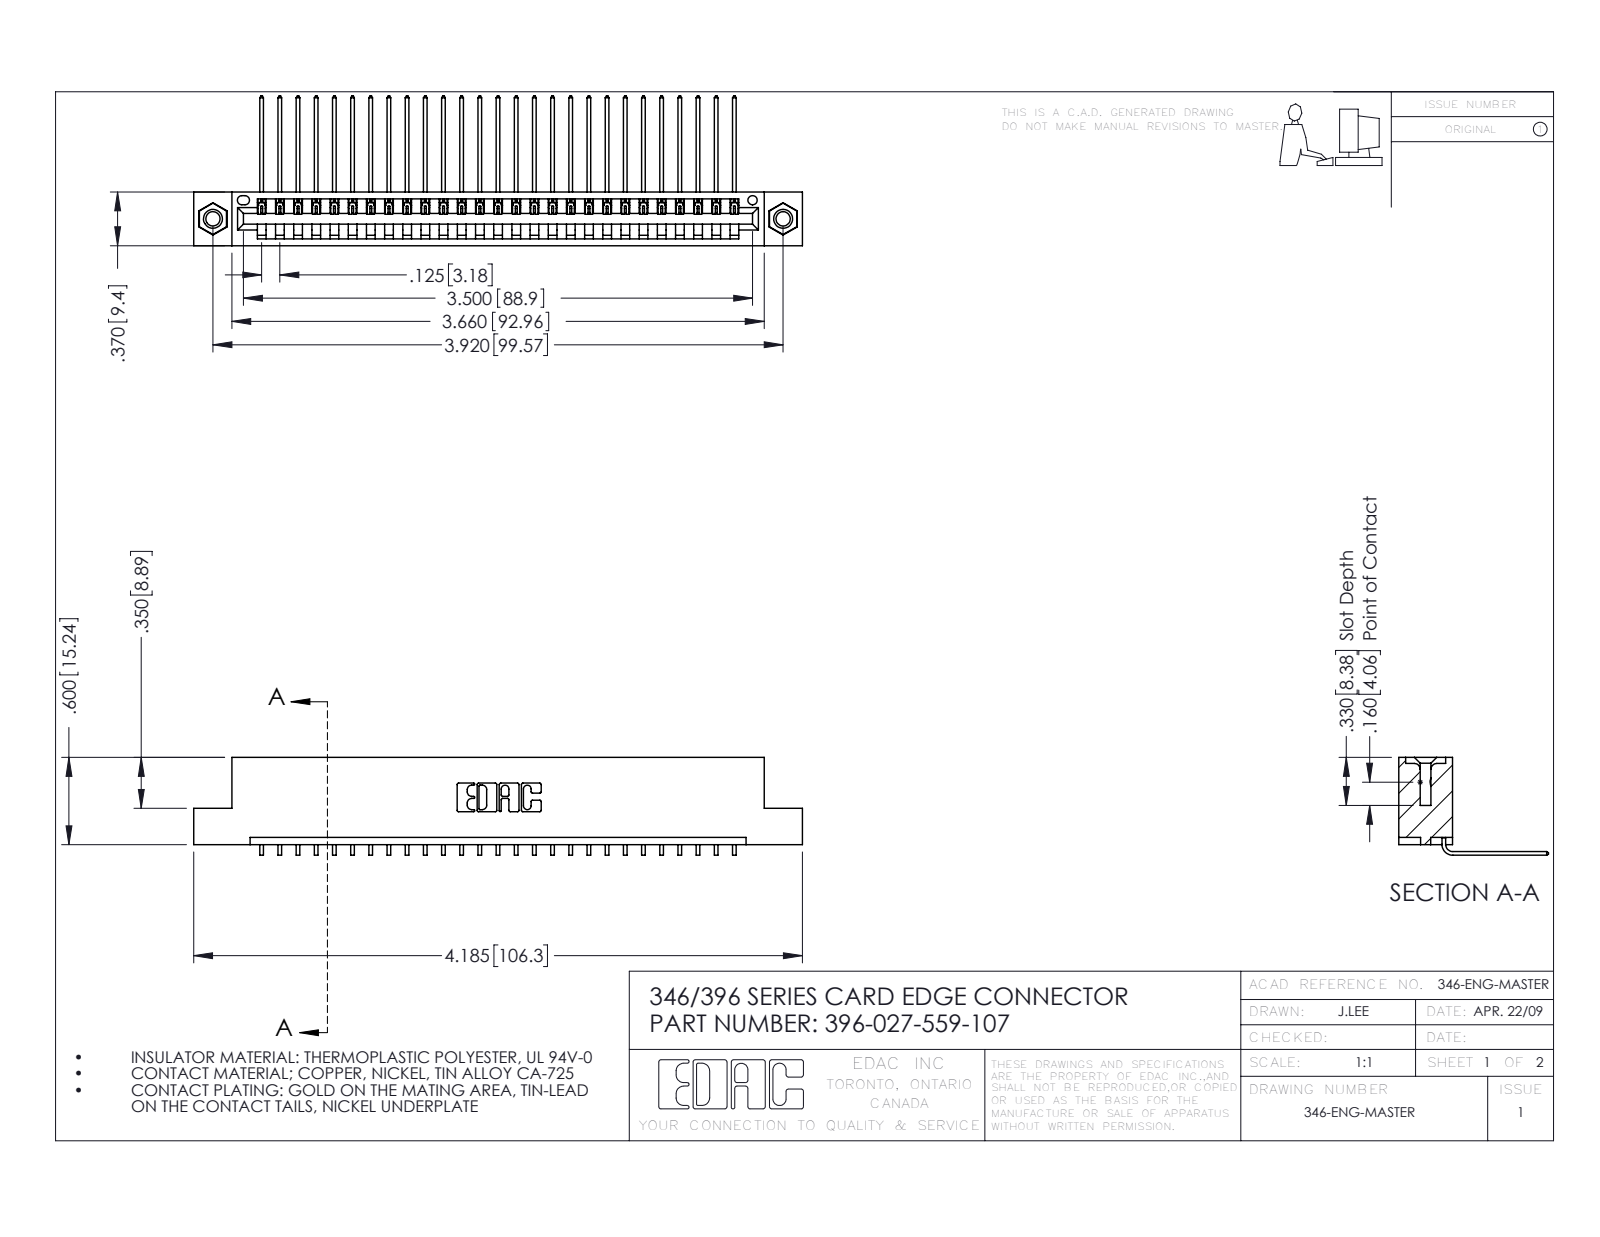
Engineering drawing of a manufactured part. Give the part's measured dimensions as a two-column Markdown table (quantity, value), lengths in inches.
| quantity | value |
| --- | --- |
| part name | 345-292-001_558 559 Tail - 1; 345-250-001_345-250-005-103; 346 Part_Flush Mounting Lugs - 0.156 Dia-TI; 396-027-559-107 |
| STEP written by | SolidWorks 2016 (CONFIG_CONTROL_DESIGN) |
| units | inches |
| bodies | 30 solids, 1802 faces (1242 planar, 544 cylindrical, 16 other) |
| overall size | 4.185 × 1.03 × 0.673 |
| volume | 0.619 in³ |
| surface area | 20.29 in² |
| round holes (diameter × count) | 0.098 × 2, 0.125 × 2, 0.156 × 2, 0.064 × 1 |
| round bosses / shafts (diameter × count) | 0.155 × 2 |
| partial cylindrical surfaces (radius × count) | 0.006 × 54, 0.01 × 22, 0.007 × 6, 0.031 × 6, 0.026 × 3, 0.031 × 2, 0.04 × 2, 0.014 × 1 |
| main face-to-face distances | 0.048, 0.322, 0.37, 0.25, 0.072, 0.025, 0.298, 0.148, 0.222, 0.1 |
| hole center spacings | 0.246, 3.712, 3.92 |
